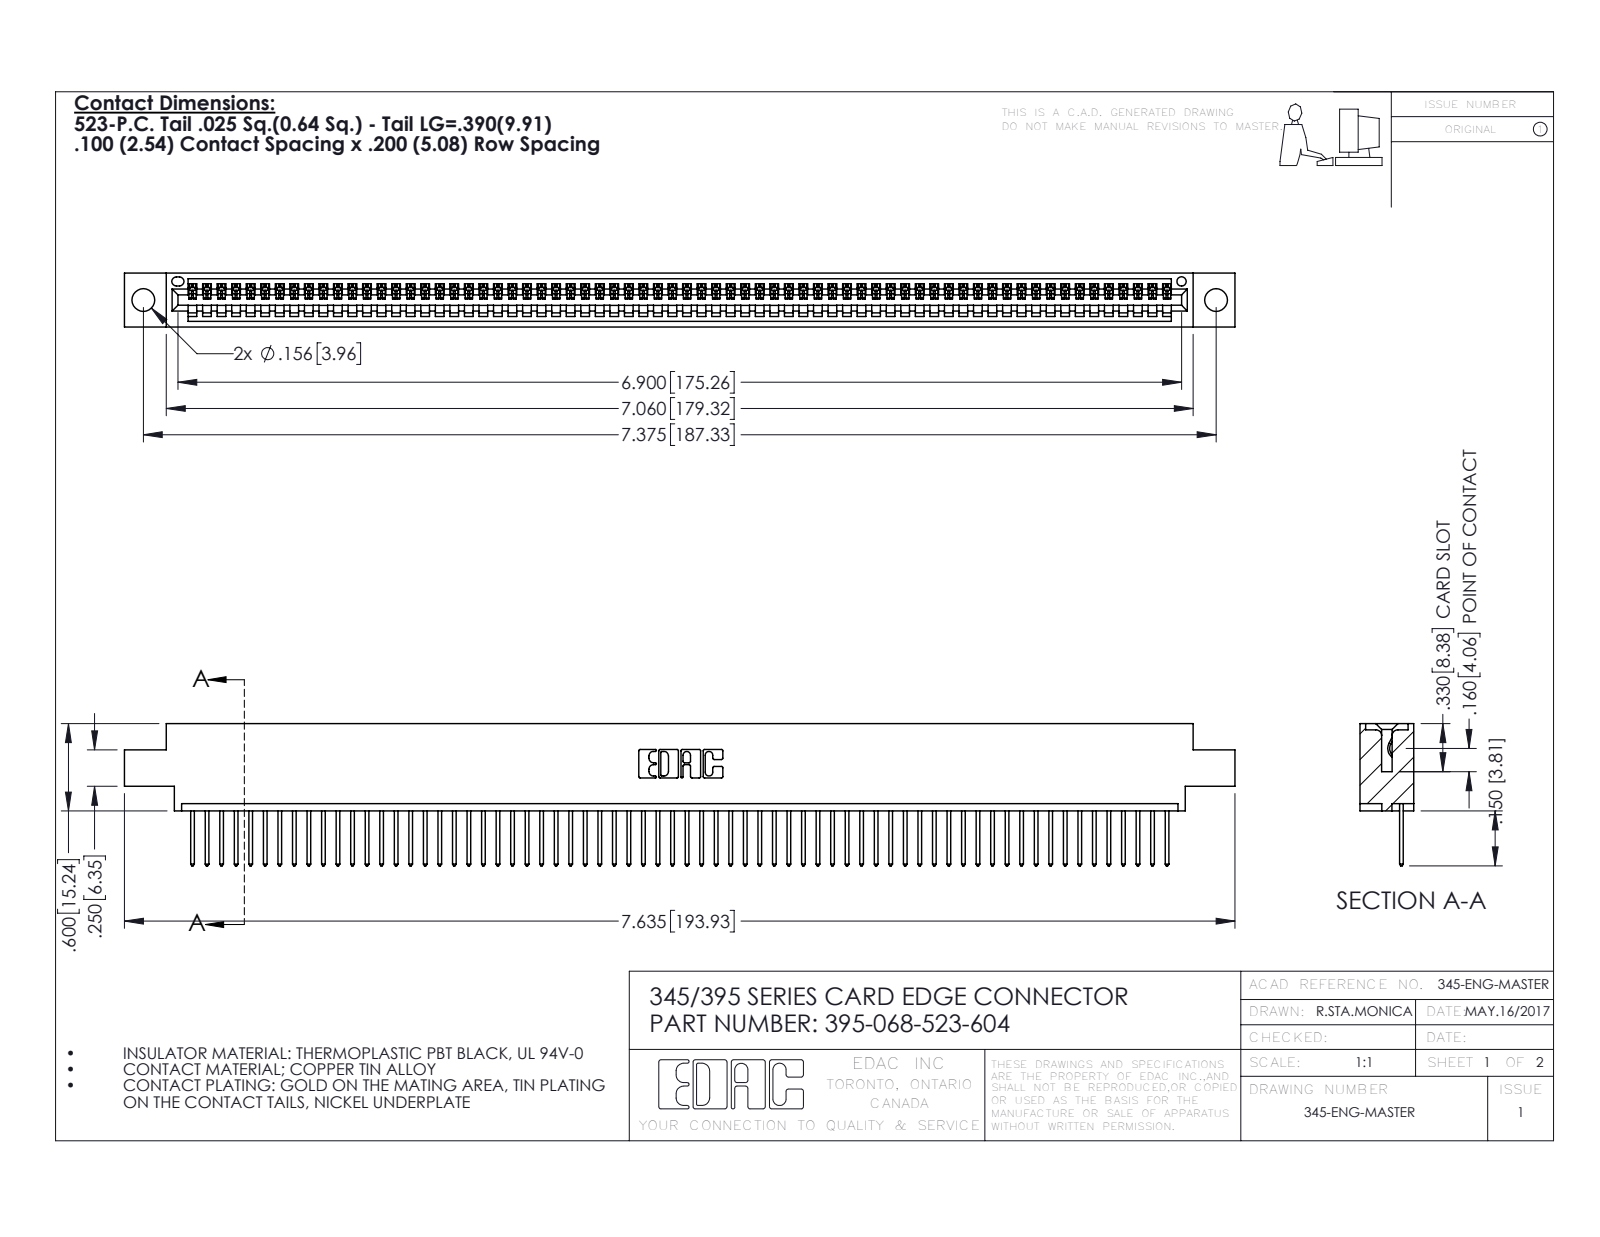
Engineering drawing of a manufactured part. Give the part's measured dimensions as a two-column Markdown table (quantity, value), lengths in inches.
| quantity | value |
| --- | --- |
| part name | 345 Part_0.170 Offset - 0.156 Dia-TH; 345-292-001_345-293-123; 395-068-523-604 |
| STEP written by | SolidWorks 2016 (CONFIG_CONTROL_DESIGN) |
| units | inches |
| bodies | 69 solids, 4074 faces (2804 planar, 1270 cylindrical, 0 other) |
| overall size | 7.635 × 0.977 × 0.37 |
| volume | 1.123 in³ |
| surface area | 38.47 in² |
| round holes (diameter × count) | 0.156 × 2, 0.064 × 1 |
| partial cylindrical surfaces (radius × count) | 0.006 × 136, 0.01 × 136, 0.01 × 22, 0.007 × 6, 0.031 × 6, 0.026 × 3, 0.031 × 2, 0.04 × 2 |
| main face-to-face distances | 0.298, 0.072, 0.37, 0.098, 0.272, 0.025, 0.2, 0.225, 0.175, 0.149 |
| hole center spacings | 0.27, 7.139, 7.375 |
